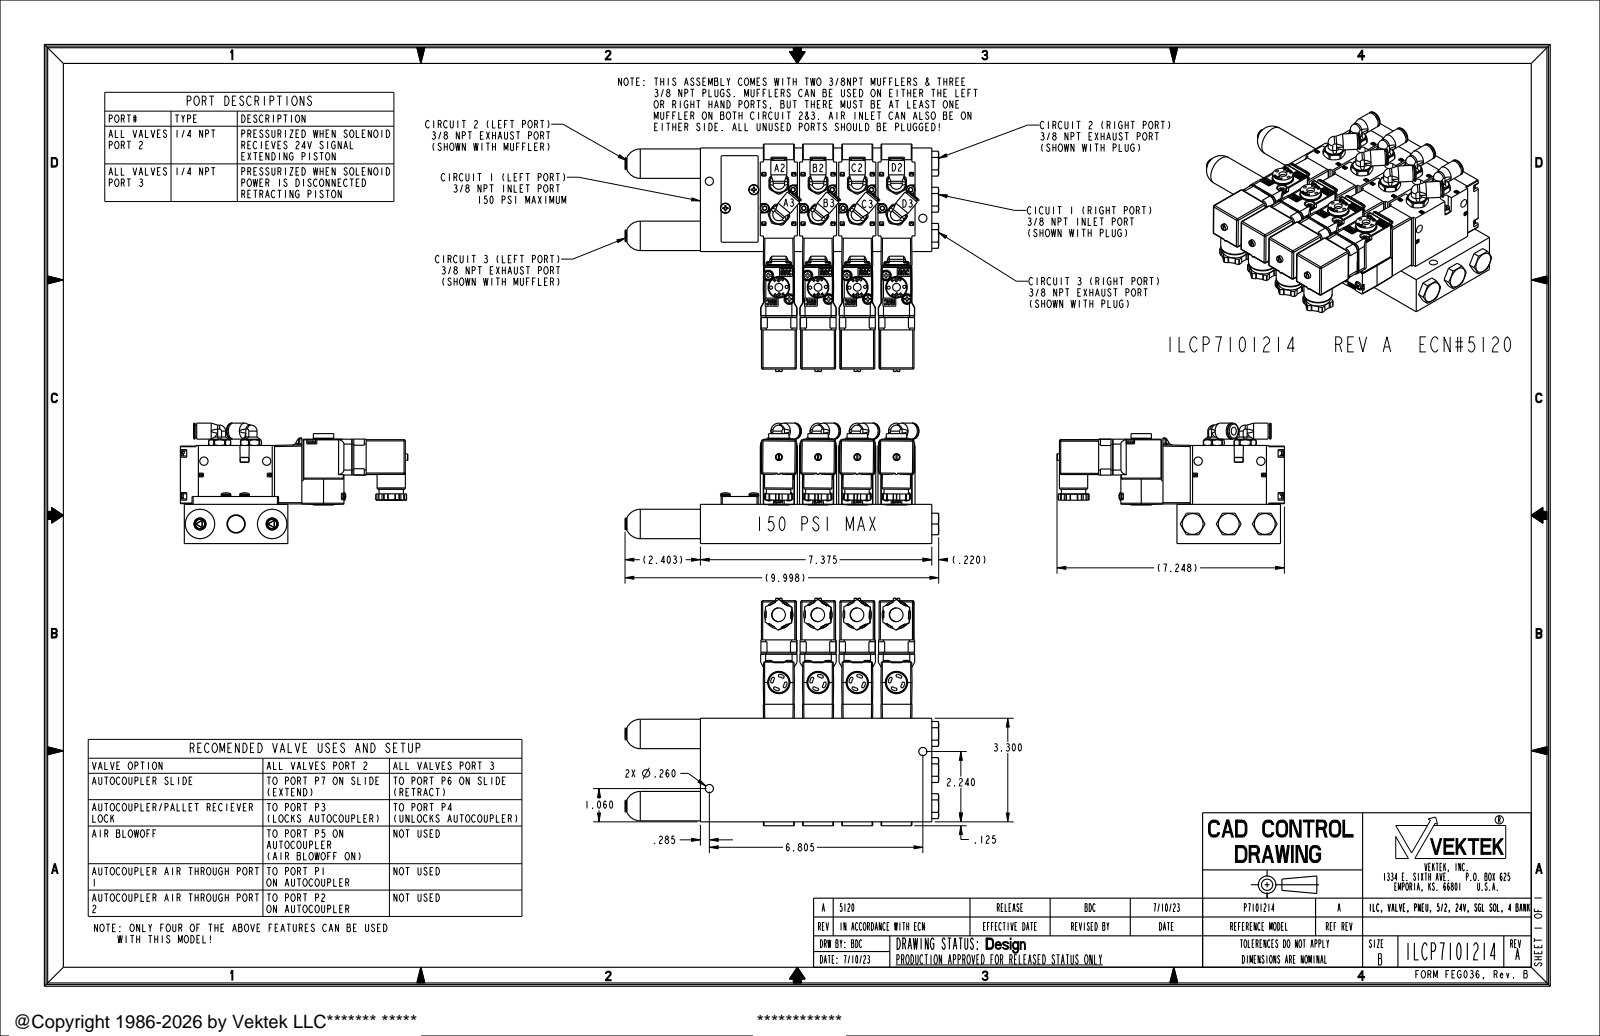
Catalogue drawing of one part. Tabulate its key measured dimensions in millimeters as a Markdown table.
| quantity | value |
| --- | --- |
| part name | ILCP7101214 |
| STEP written by | CREO PARAMETRIC BY PTC INC, 2021164 (AUTOMOTIVE_DESIGN) |
| units | millimeters |
| bodies | 5 solids, 5442 faces (2936 planar, 1294 cylindrical, 1212 other) |
| overall size | 253.9 × 184.1 × 97.5 |
| volume | 1 439 000 mm³ |
| surface area | 226 900 mm² |
| round holes (diameter × count) | 3.5 × 16, 6.4 × 16, 2.5 × 8, 2.8 × 8, 3.2 × 8, 6.5 × 8, 7.3 × 8, 2.7 × 4, 2.8 × 4, 6 × 4, 6.3 × 4, 11.1 × 4 |
| round bosses / shafts (diameter × count) | 7 × 24, 6.5 × 16, 9.5 × 10, 16.5 × 8, 14.8 × 8, 13 × 8, 6.8 × 8, 22.9 × 4 |
| partial cylindrical surfaces (radius × count) | 0.2 × 96, 1 × 80, 0.3 × 56, 0.5 × 49, 4 × 48, 0.8 × 43, 0.9 × 32, 1.1 × 32 |
| main face-to-face distances | 31.8, 63.5, 95.3, 30, 61.7, 1.8, 31.8, 83.8, 33.5, 27.5 |
| hole center spacings | 31.8, 63.5, 95.3, 26.2, 53.4, 25.4, 40.7, 57.9 |
